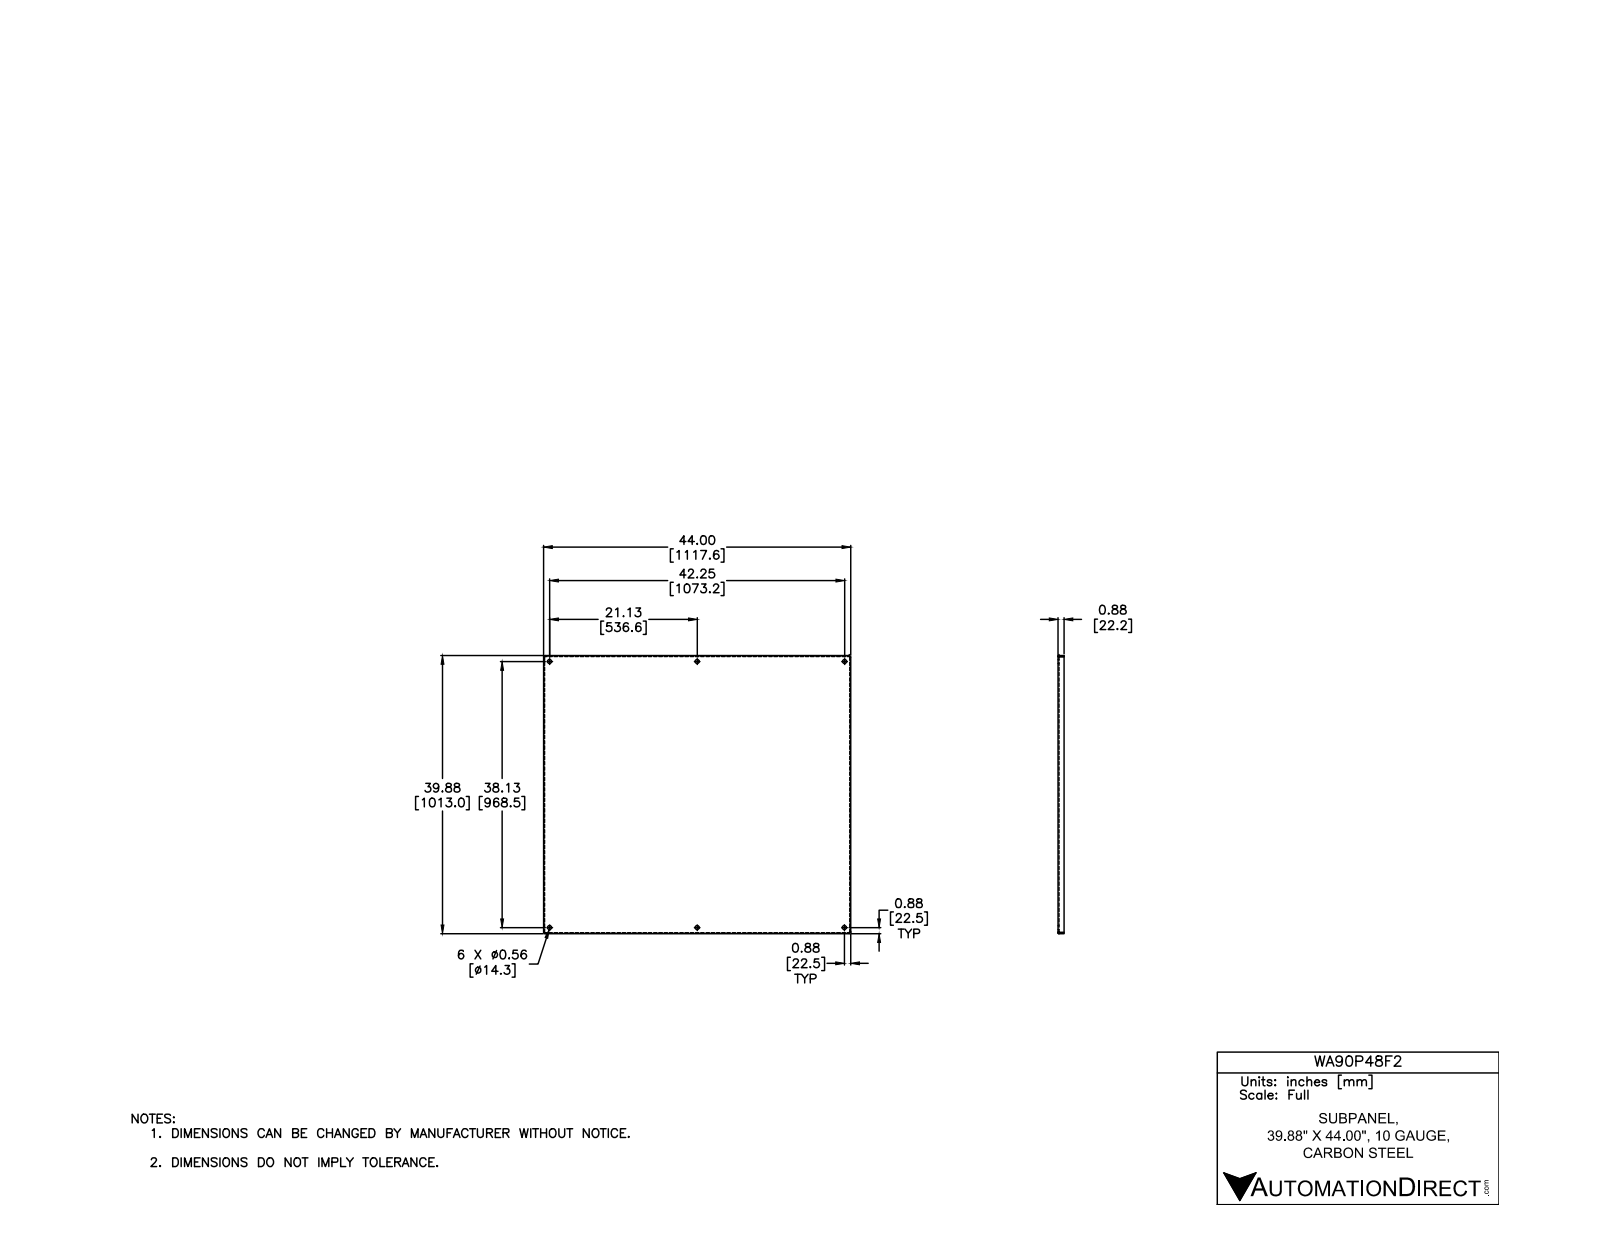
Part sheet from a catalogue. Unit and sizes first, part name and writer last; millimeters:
Units: millimetres
Overall size (bounding box): 1117.6 × 1013.2 × 22.2
Round holes (diameter × count): ⌀14.3 ×6
Partial cylindrical surfaces — rounded edges, fillets, slot ends (radius × count): R0.8 ×4, R4 ×4
Main face-to-face distances: 3.2, 1010, 3.2, 1114.4, 1013.2, 1006.8, 1117.6, 1111.3, 19.1, 22.2
Hole centre spacings: 536.6, 968.7, 1107.4, 1107.4, 536.6, 968.7, 1073.2, 1073.2
Volume: 3 833 000 mm³ · Surface area: 2 430 000 mm²
Bodies: 1 solid, 44 faces (22 planar, 14 cylindrical, 8 other)
Part name (STEP PRODUCT): WA_P_F
STEP written by: Autodesk Inventor 2012 (AUTOMOTIVE_DESIGN)
